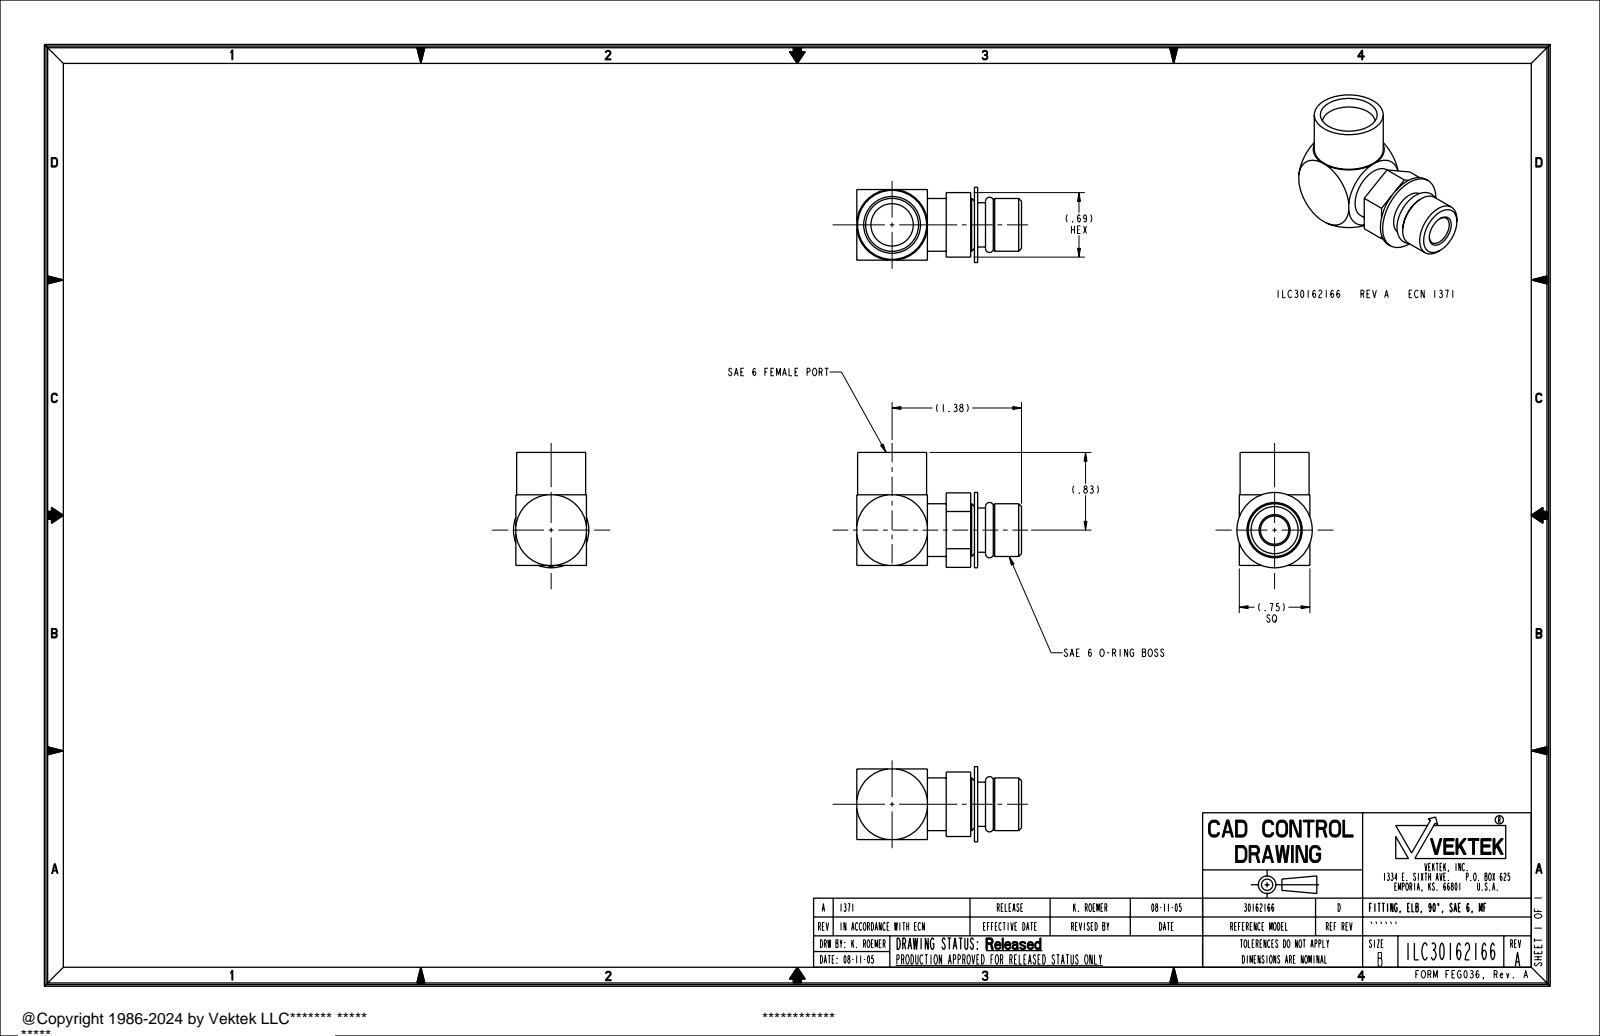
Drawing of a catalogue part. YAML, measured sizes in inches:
part_name: "ILC30162166"
step_written_by: "PRO/ENGINEER BY PARAMETRIC TECHNOLOGY CORPORATION, 2004290 (AUTOMOTIVE_DESIGN_CC2)"
units: inches
bodies: {solids: 1, faces: 58, planar: 20, cylindrical: 18, other: 20}
overall_size: [1.75, 1.225, 0.8]
volume: 0.577
surface_area: 9.764
round_holes:
  - {diameter: 0.3, count: 1}
  - {diameter: 0.45, count: 1}
  - {diameter: 0.563, count: 1}
round_bosses_or_shafts:
  - {diameter: 0.8, count: 1}
  - {diameter: 0.733, count: 1}
  - {diameter: 0.56, count: 1}
  - {diameter: 0.47, count: 1}
face_to_face_distances: [0.75, 1.284, 0.5, 0.685, 1.25, 0.034, 0.032, 0.717, 0.75, 0.534]
